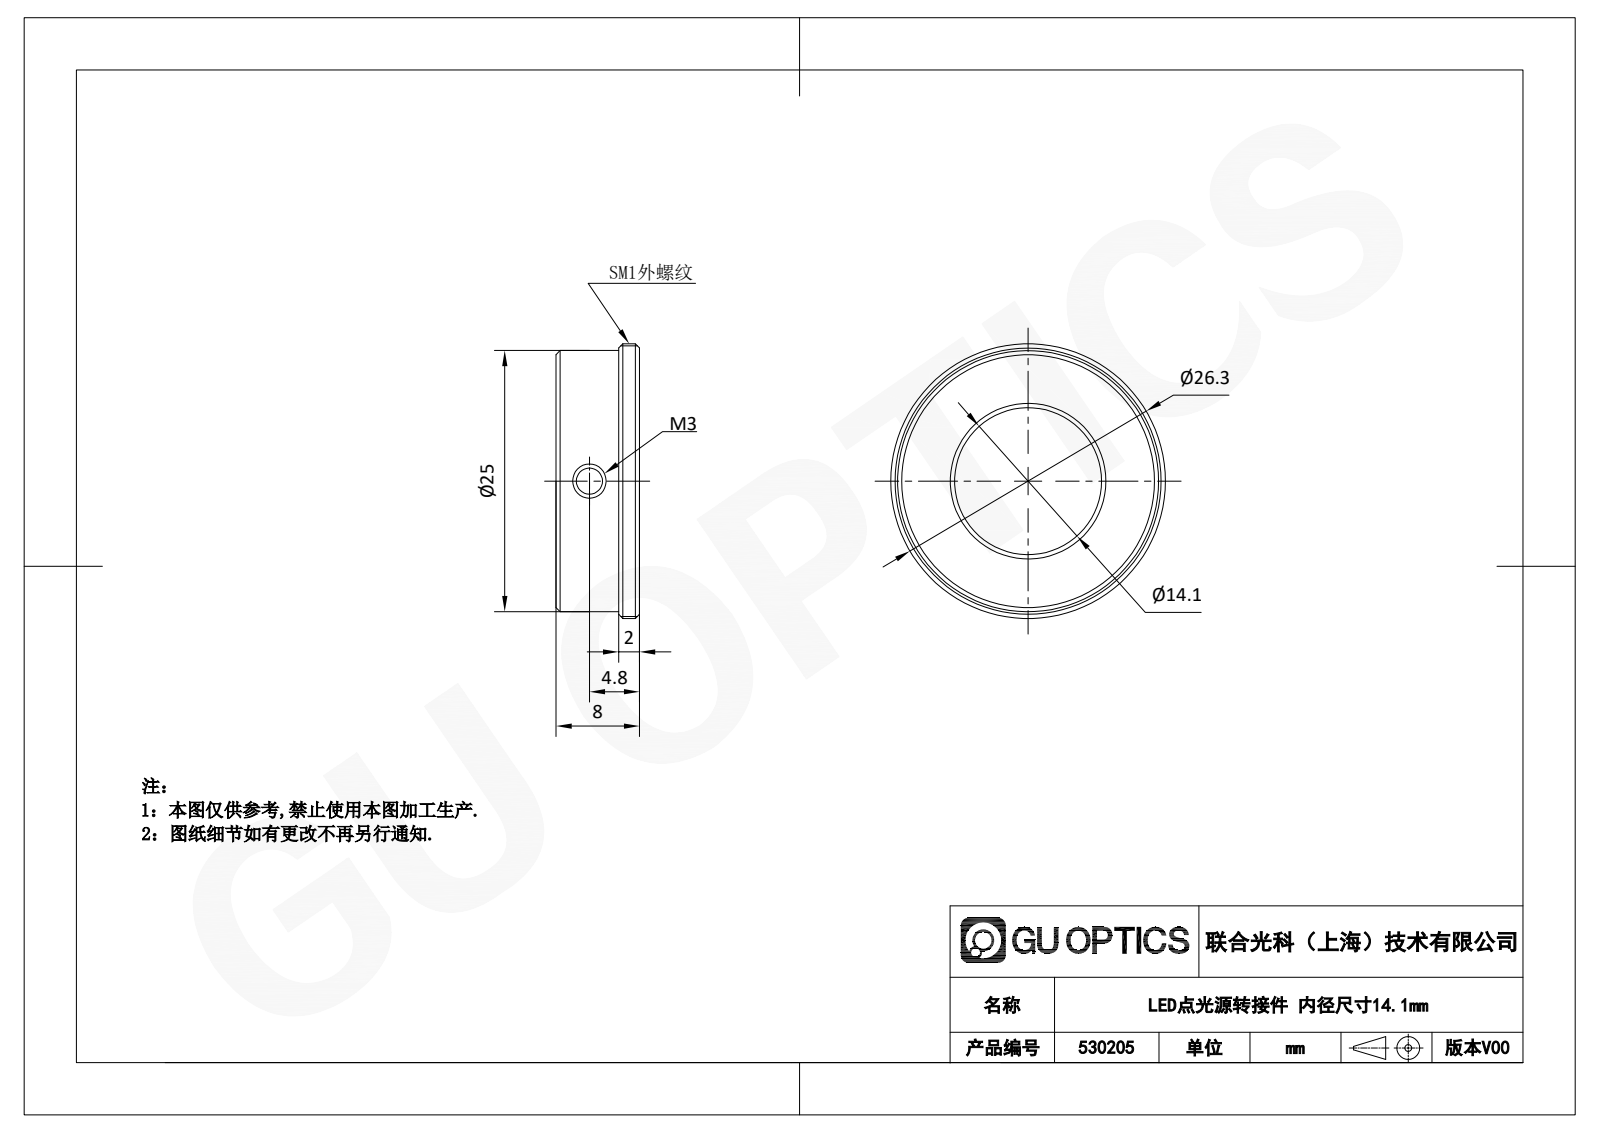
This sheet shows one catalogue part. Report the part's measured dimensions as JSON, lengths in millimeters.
{"part_name": "530205", "step_written_by": "SolidWorks 2020 (CONFIG_CONTROL_DESIGN)", "units": "millimeters", "bodies": {"solids": 1, "faces": 13, "planar": 3, "cylindrical": 4, "other": 6}, "overall_size": [26.29, 26.29, 8], "volume_mm3": 2728, "surface_area_mm2": 1718, "round_holes": [[2.5, 1], [14.1, 1]], "round_bosses_or_shafts": [[26.29, 1], [25, 1]], "face_to_face_distances": [8, 2, 6]}
